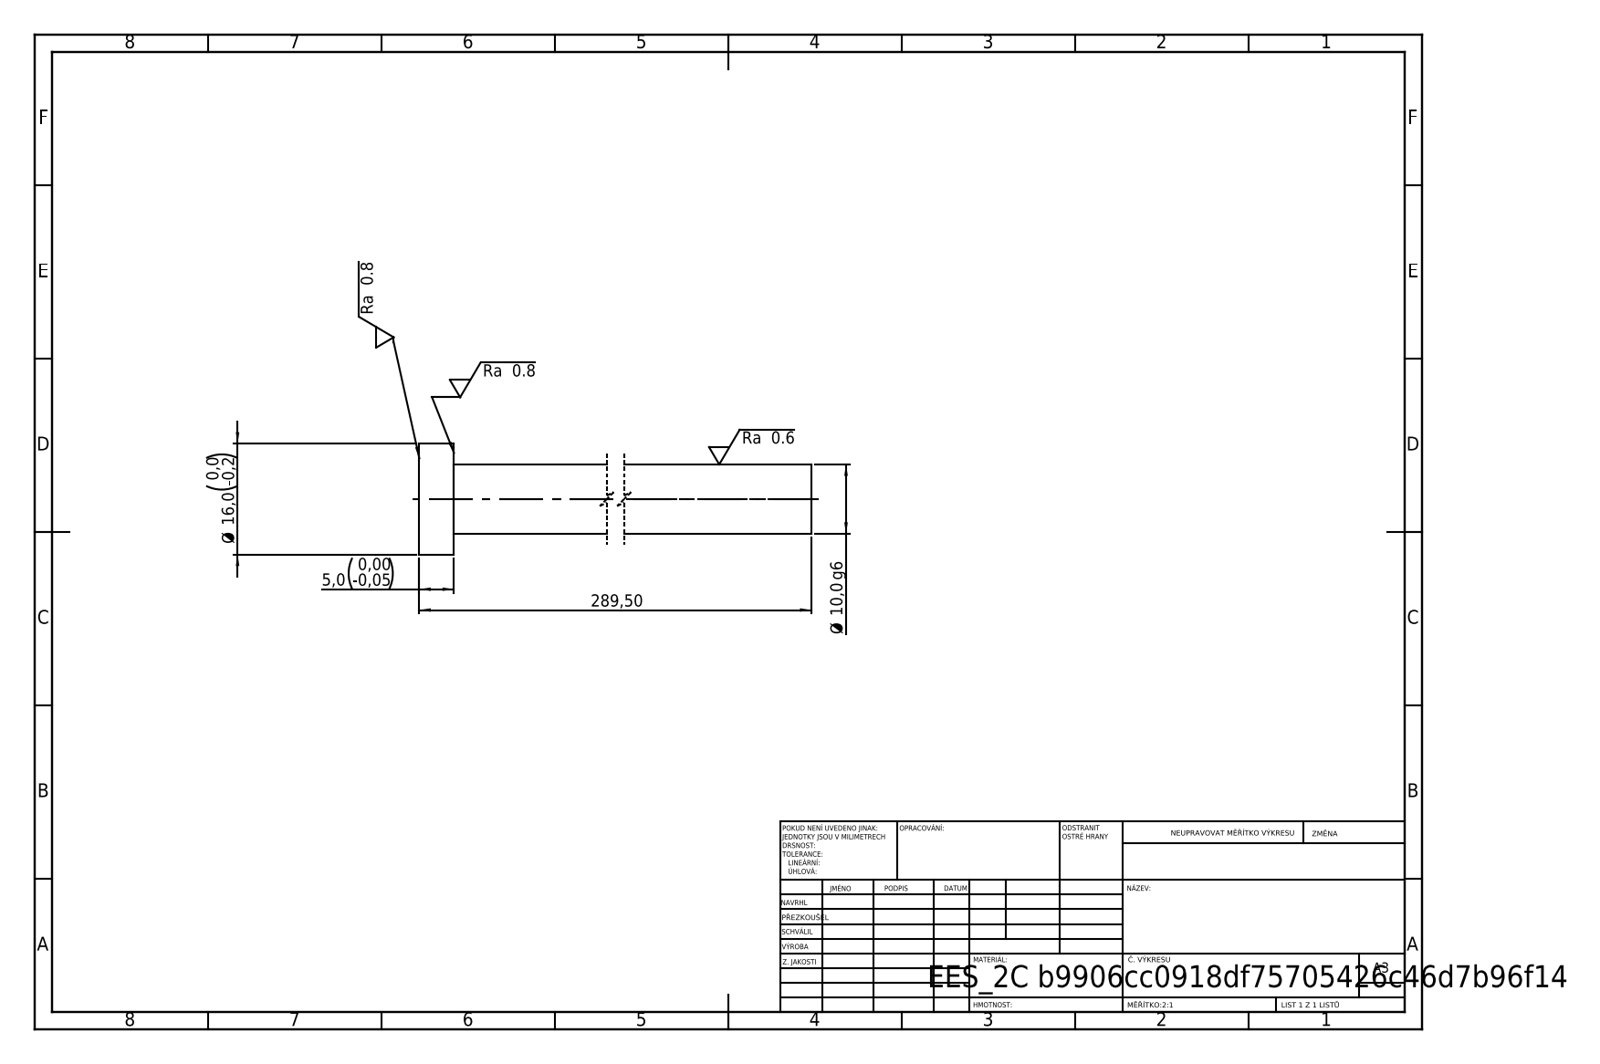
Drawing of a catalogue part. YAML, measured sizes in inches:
step_written_by: "SolidWorks 2019 (CONFIG_CONTROL_DESIGN)"
units: inches
bodies: {solids: 1, faces: 7, planar: 3, cylindrical: 4, other: 0}
overall_size: [11.398, 0.63, 0.63]
volume: 1.425
surface_area: 14.87
round_bosses_or_shafts:
  - {diameter: 0.63, count: 1}
  - {diameter: 0.394, count: 1}
face_to_face_distances: [0.197, 11.398, 11.201]
